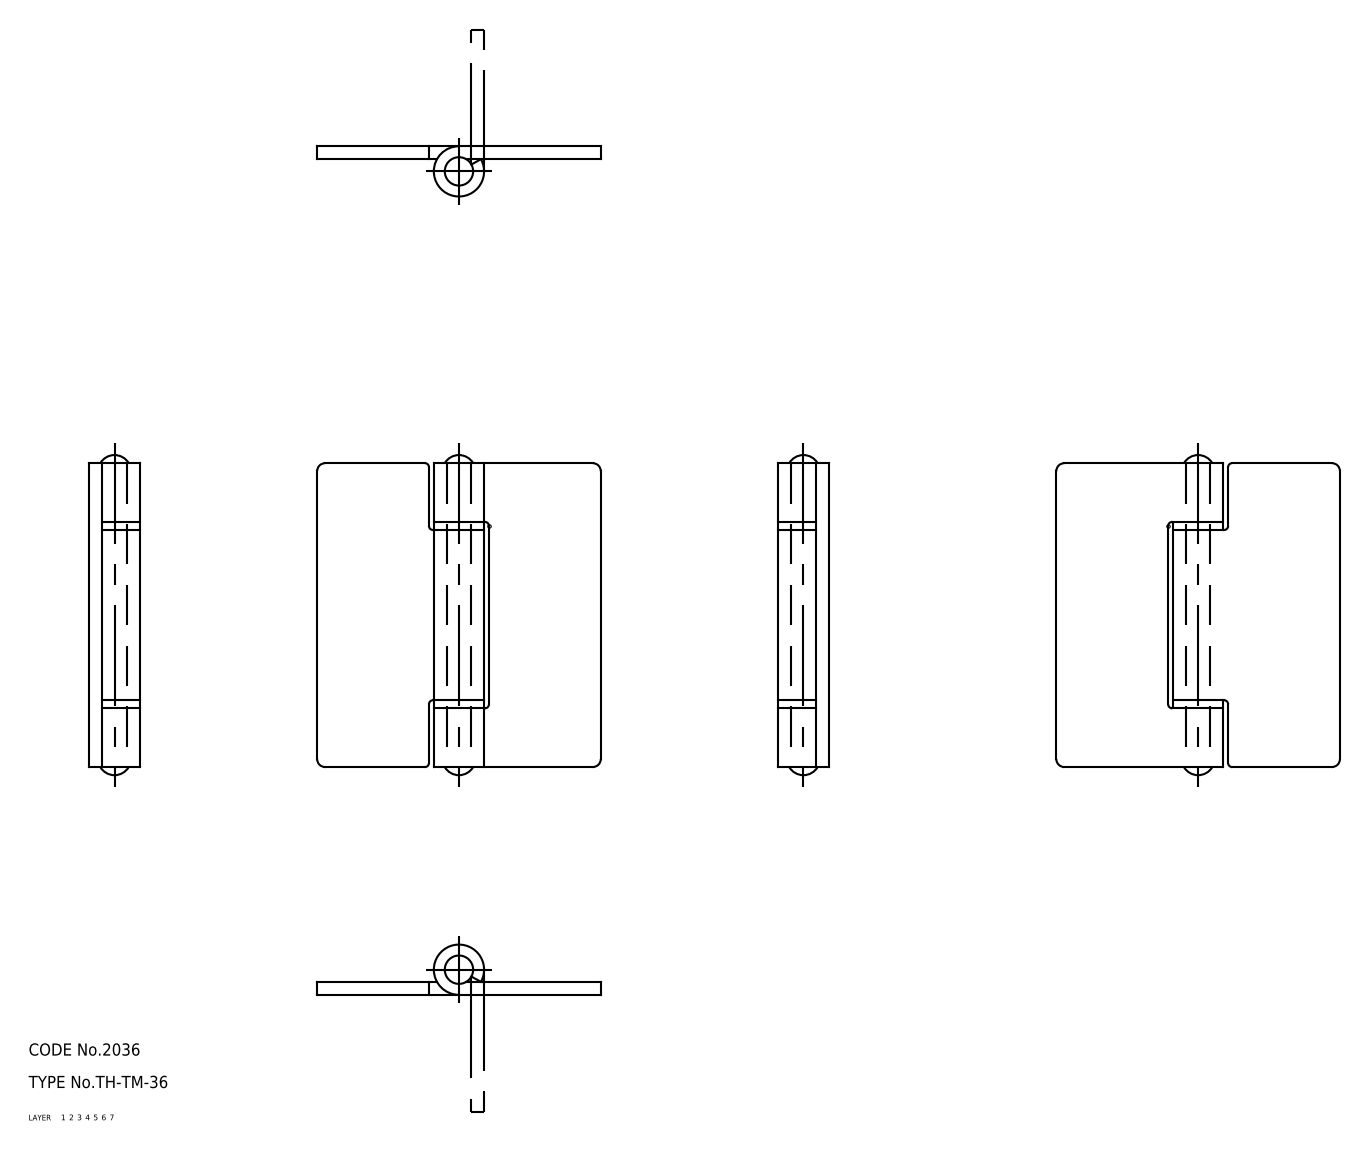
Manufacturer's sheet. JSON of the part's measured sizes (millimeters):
{"part_name": "hinge piece_B; hinge piece_A; washer; shaft (+1 more)", "step_written_by": "CADfix (AUTOMOTIVE_DESIGN)", "units": "millimeters", "bodies": {"solids": 5, "faces": 54, "planar": 0, "cylindrical": 0, "other": 54}, "overall_size": [78.96, 70, 12.4], "volume_mm3": 22944, "surface_area_mm2": 16762}
